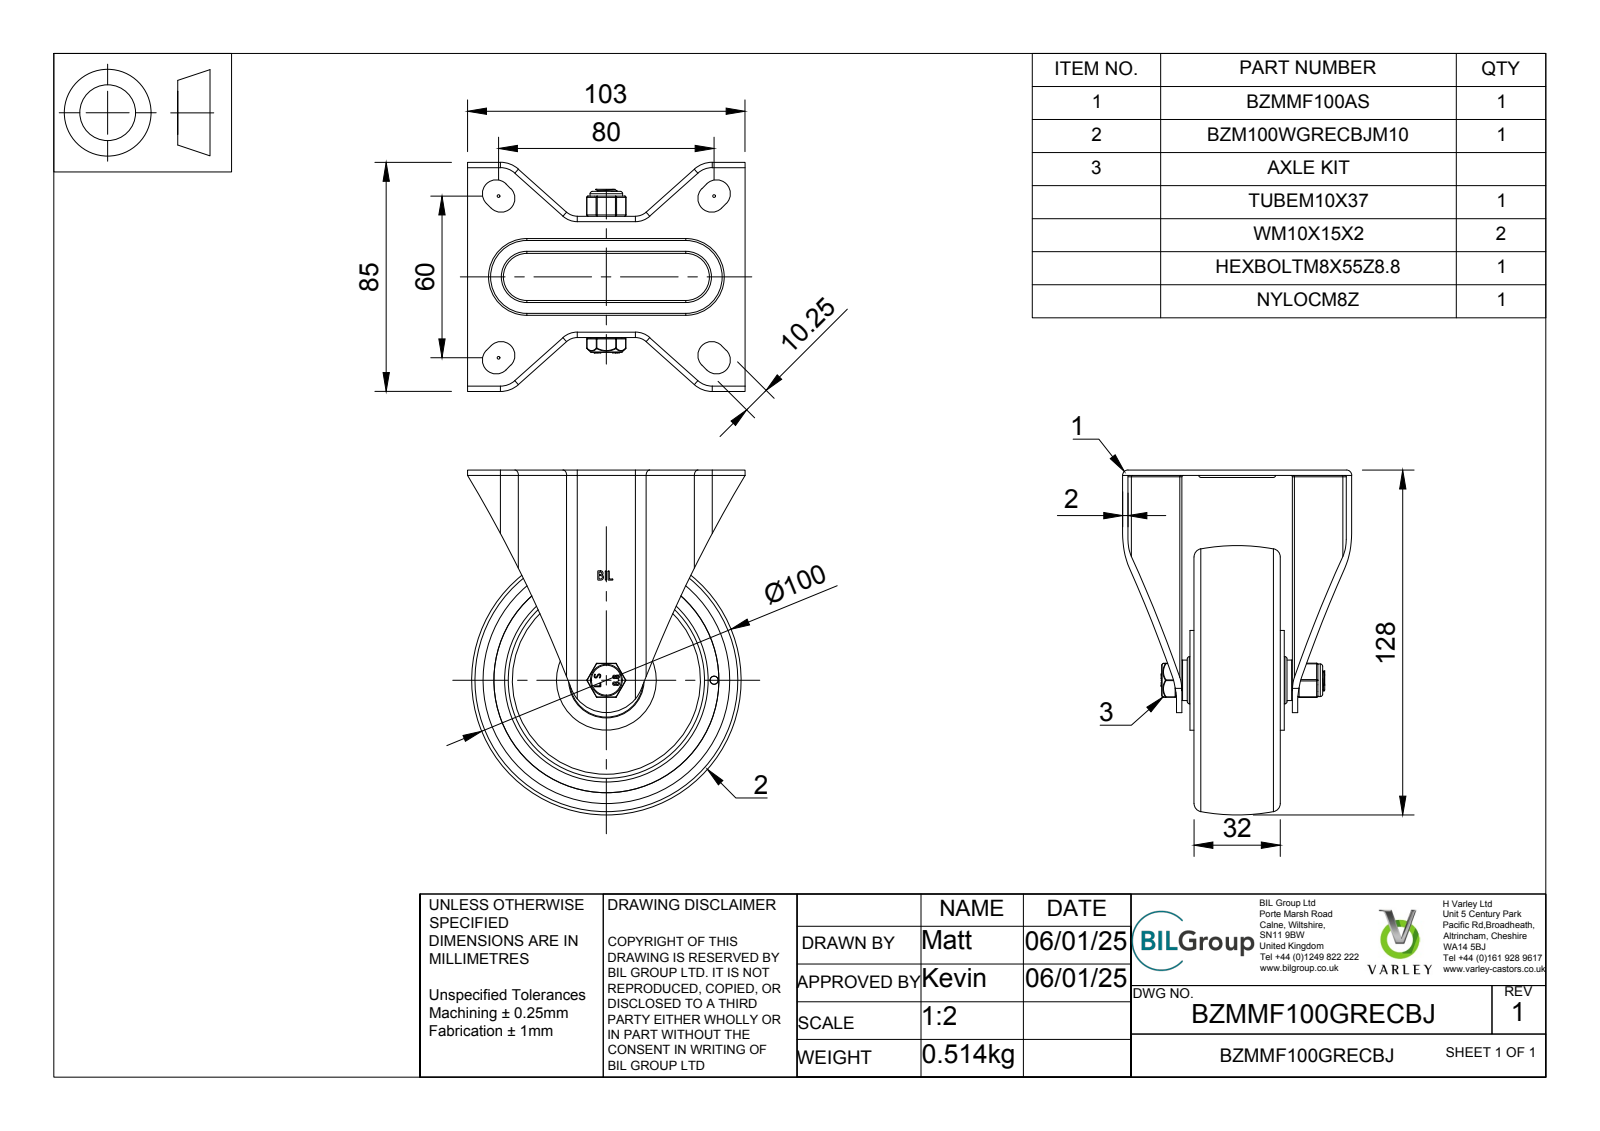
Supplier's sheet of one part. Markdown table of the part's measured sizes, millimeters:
| quantity | value |
| --- | --- |
| part name | BZMMF100GRECBJ v3; BZM100WGRECBJM10 v1; POLYPROPYLENE RIM; GREY ELECTRICALLY CONDUCTIVE RUBBER TYRE (+7 more) |
| STEP written by | Autodesk Translation Framework v13.20.0.188 (AP242_MANAGED_MODEL_BASED_3D_ENGINEERING_MIM_LF) |
| units | millimeters |
| bodies | 28 solids, 464 faces (146 planar, 184 cylindrical, 134 other) |
| overall size | 128 × 103 × 85 |
| volume | 195 500 mm³ |
| surface area | 103 148 mm² |
| round holes (diameter × count) | 0.66 × 2, 3 × 1, 8 × 1, 8.2 × 1, 8.25 × 1, 8.6 × 1, 10.1 × 1, 10.25 × 1, 18 × 1, 18.6 × 1, 25.5 × 1, 28 × 1 |
| round bosses / shafts (diameter × count) | 37 × 1, 17.5 × 1, 15 × 1, 12.1 × 1, 11.5 × 1, 10 × 1, 7.87 × 1, 6.45 × 1 |
| partial cylindrical surfaces (radius × count) | 0.5 × 26, 0.25 × 12, 0.75 × 8, 2 × 8, 5.12 × 8, 0.33 × 4, 0.64 × 4, 3 × 4 |
| main face-to-face distances | 2, 20, 14.26, 18, 23, 13.5, 18.5, 43, 5, 25 |
| hole center spacings | 3.22, 37.05, 2.49, 40 |
